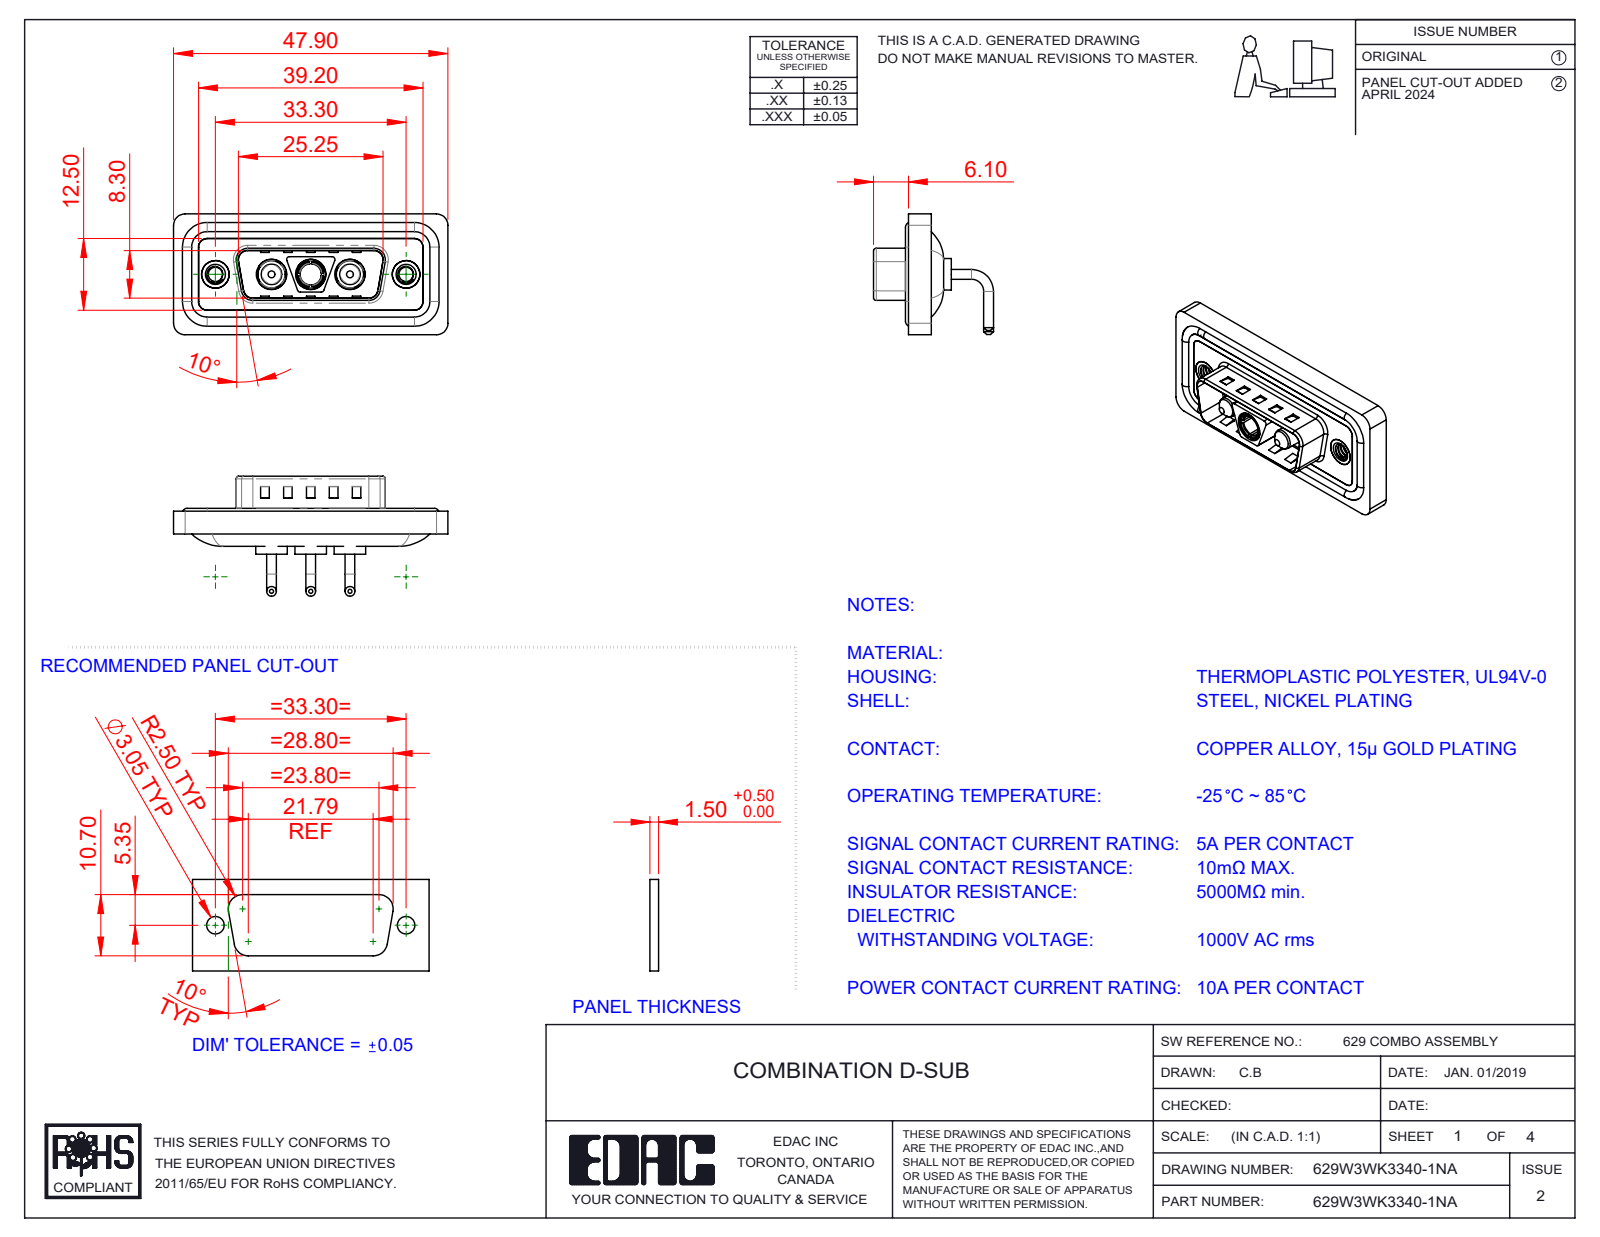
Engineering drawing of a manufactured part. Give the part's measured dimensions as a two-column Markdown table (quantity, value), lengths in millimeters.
| quantity | value |
| --- | --- |
| part name | 629Combo Housing_3WK3; 629Combo Waterproof Housing_15 Contacts; 629Combo Threaded Rivet_A; Power Pin_10A RA (+4 more) |
| STEP written by | SolidWorks 2023 (CONFIG_CONTROL_DESIGN) |
| units | millimeters |
| bodies | 13 solids, 615 faces (231 planar, 254 cylindrical, 130 other) |
| overall size | 47.9 × 21.1 × 20.95 |
| volume | 5 712 mm³ |
| surface area | 9 264 mm² |
| round holes (diameter × count) | 4.85 × 3, 5.3 × 3, 2.5 × 2, 4 × 2, 4.8 × 2, 5 × 2, 3.7 × 1 |
| round bosses / shafts (diameter × count) | 1.7 × 6, 1.6 × 4, 5.5 × 3, 5.2 × 3, 4.75 × 3, 3.75 × 3, 4.9 × 2, 3.6 × 2 |
| partial cylindrical surfaces (radius × count) | 2 × 20, 1.5 × 18, 0.5 × 12, 1.6 × 8, 0.25 × 4, 0.6 × 4, 0.65 × 4, 0.9 × 4 |
| main face-to-face distances | 0.4, 2.9, 0.8, 1.1, 2.1, 1.6, 4.5, 3.1, 2.5, 1.5 |
| hole center spacings | 6.85, 9.8, 16.65, 23.5, 13.7, 33.3 |
